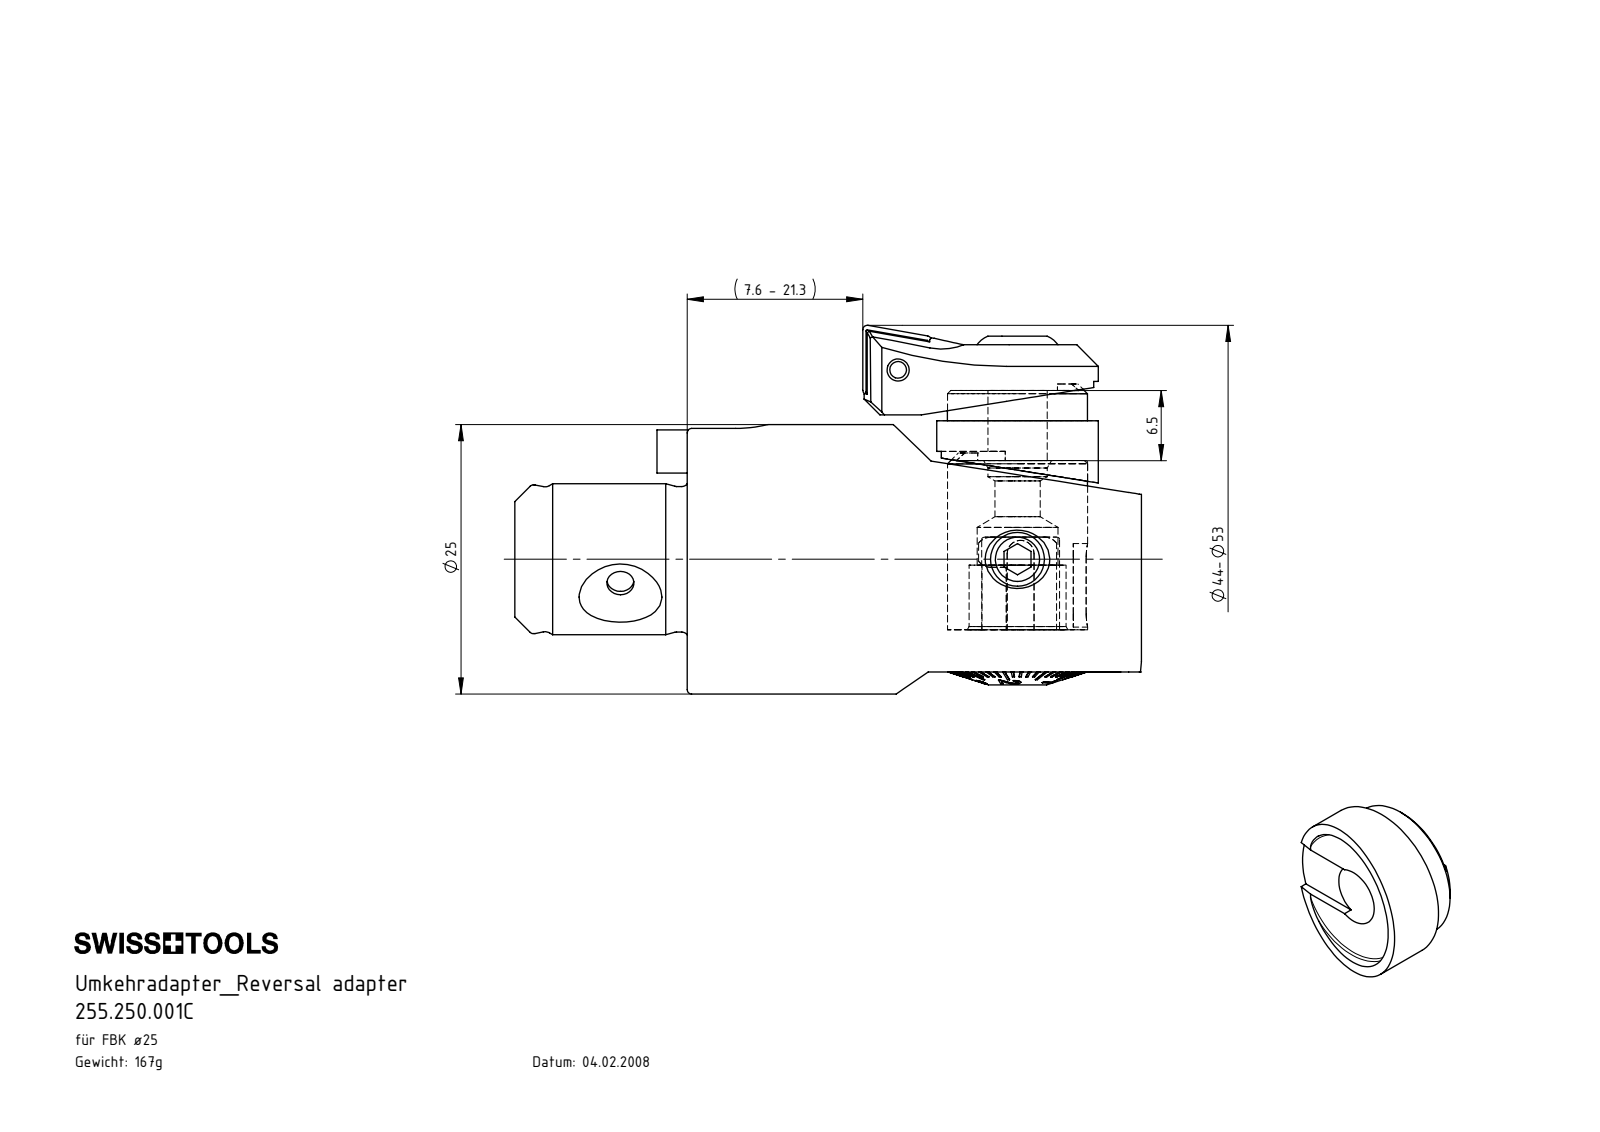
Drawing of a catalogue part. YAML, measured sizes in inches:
part_name: "F25-U00.001.006_B; 255.250.001C"
step_written_by: "SolidWorks 2017 (CONFIG_CONTROL_DESIGN)"
units: inches
bodies: {solids: 1, faces: 27, planar: 11, cylindrical: 11, other: 5}
overall_size: [0.591, 0.591, 0.361]
volume: 0.055
surface_area: 1.22
round_holes:
  - {diameter: 0.217, count: 1}
  - {diameter: 0.512, count: 1}
round_bosses_or_shafts:
  - {diameter: 0.591, count: 1}
partial_cylinders:
  - {radius: 0.02, count: 2}
face_to_face_distances: [0.256, 0.11, 0.146, 0.222, 0.112, 0.033, 0.024, 0.134, 0.246, 0.28]
